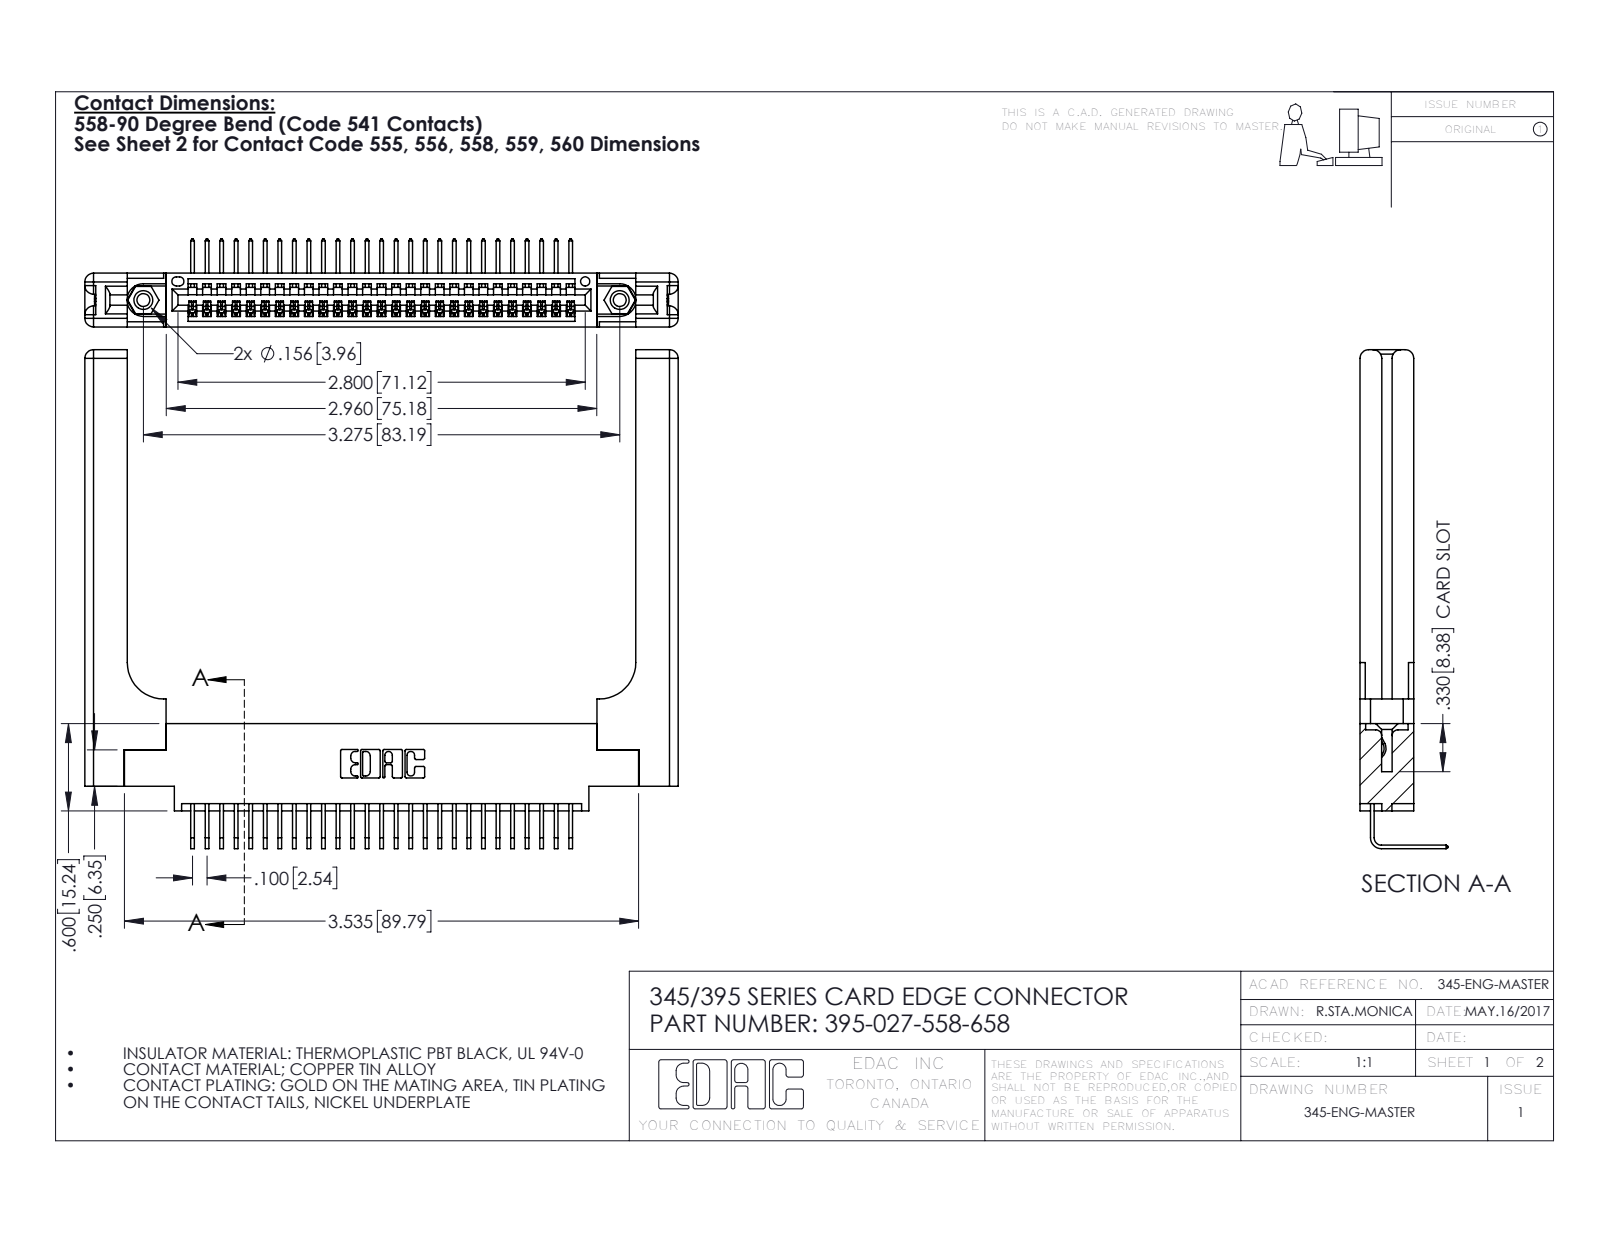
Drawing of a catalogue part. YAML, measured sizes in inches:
part_name: "345-292-001_558 Tail - 2; 345-250-001_345-250-001-102; 345 Part_0.170 Offset - 0.156 Dia-TH; 395-027-558-658 (+1 more)"
step_written_by: "SolidWorks 2016 (CONFIG_CONTROL_DESIGN)"
units: inches
bodies: {solids: 32, faces: 2006, planar: 1366, cylindrical: 580, other: 60}
overall_size: [4.079, 3.429, 0.605]
volume: 1.111
surface_area: 28.89
round_holes:
  - {diameter: 0.089, count: 2}
  - {diameter: 0.125, count: 2}
  - {diameter: 0.156, count: 2}
  - {diameter: 0.064, count: 1}
round_bosses_or_shafts:
  - {diameter: 0.155, count: 2}
partial_cylinders:
  - {radius: 0.006, count: 54}
  - {radius: 0.01, count: 22}
  - {radius: 0.06, count: 16}
  - {radius: 0.007, count: 6}
  - {radius: 0.031, count: 6}
  - {radius: 0.026, count: 3}
  - {radius: 0.03, count: 2}
  - {radius: 0.031, count: 2}
face_to_face_distances: [0.37, 0.072, 0.298, 0.148, 0.15, 0.098, 0.272, 0.025, 0.2, 0.077]
hole_center_spacings: [0.27, 3.04, 3.275]
